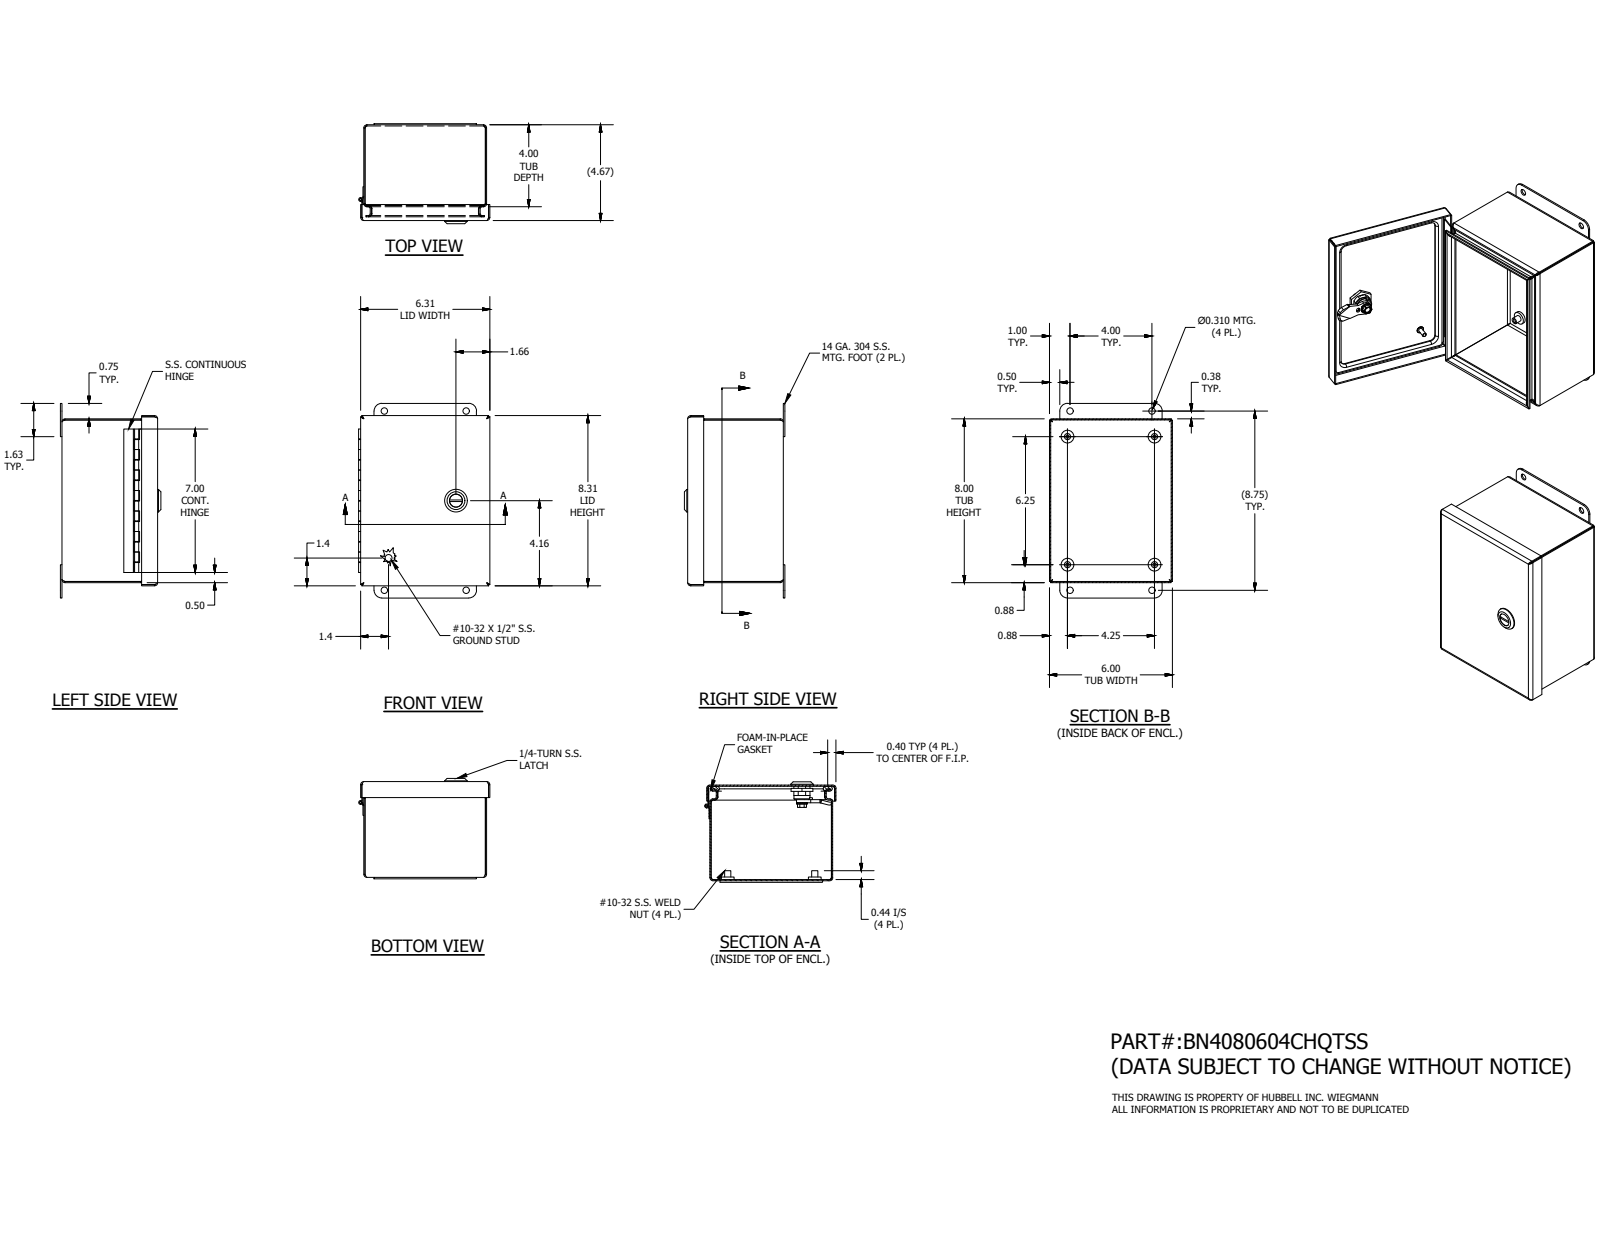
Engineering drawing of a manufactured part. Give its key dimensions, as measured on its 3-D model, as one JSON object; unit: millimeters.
{"part_name": "BN40806CHQTSSLID; 8x6; 34853; H4050547LH (+8 more)", "step_written_by": "Autodesk Inventor 2016 (AUTOMOTIVE_DESIGN)", "units": "millimeters", "bodies": {"solids": 19, "faces": 588, "planar": 311, "cylindrical": 183, "other": 94}, "overall_size": [241.3, 162.86, 124.59], "volume_mm3": 322400, "surface_area_mm2": 395141, "round_holes": [[3.96, 4], [7.87, 4], [2.96, 1], [5, 1], [8, 1], [10, 1], [10.2, 1], [16.1, 1]], "round_bosses_or_shafts": [[15.88, 4], [7.62, 4], [28, 1], [19.8, 1], [16, 1], [15.2, 1], [13.5, 1], [12.8, 1]], "partial_cylinders_radius": [[2.38, 20], [3.88, 20], [3.17, 16], [0.5, 8], [4, 4], [9.53, 4], [2.31, 2], [6.45, 1]], "face_to_face_distances": [1.5, 1.49, 117.19, 118.68, 115.69, 117.18, 201.7, 152.4, 150.9, 150.91], "hole_center_spacings": [31.91, 109.48, 190.53, 217.41, 101.6, 107.95, 158.75, 191.98]}
